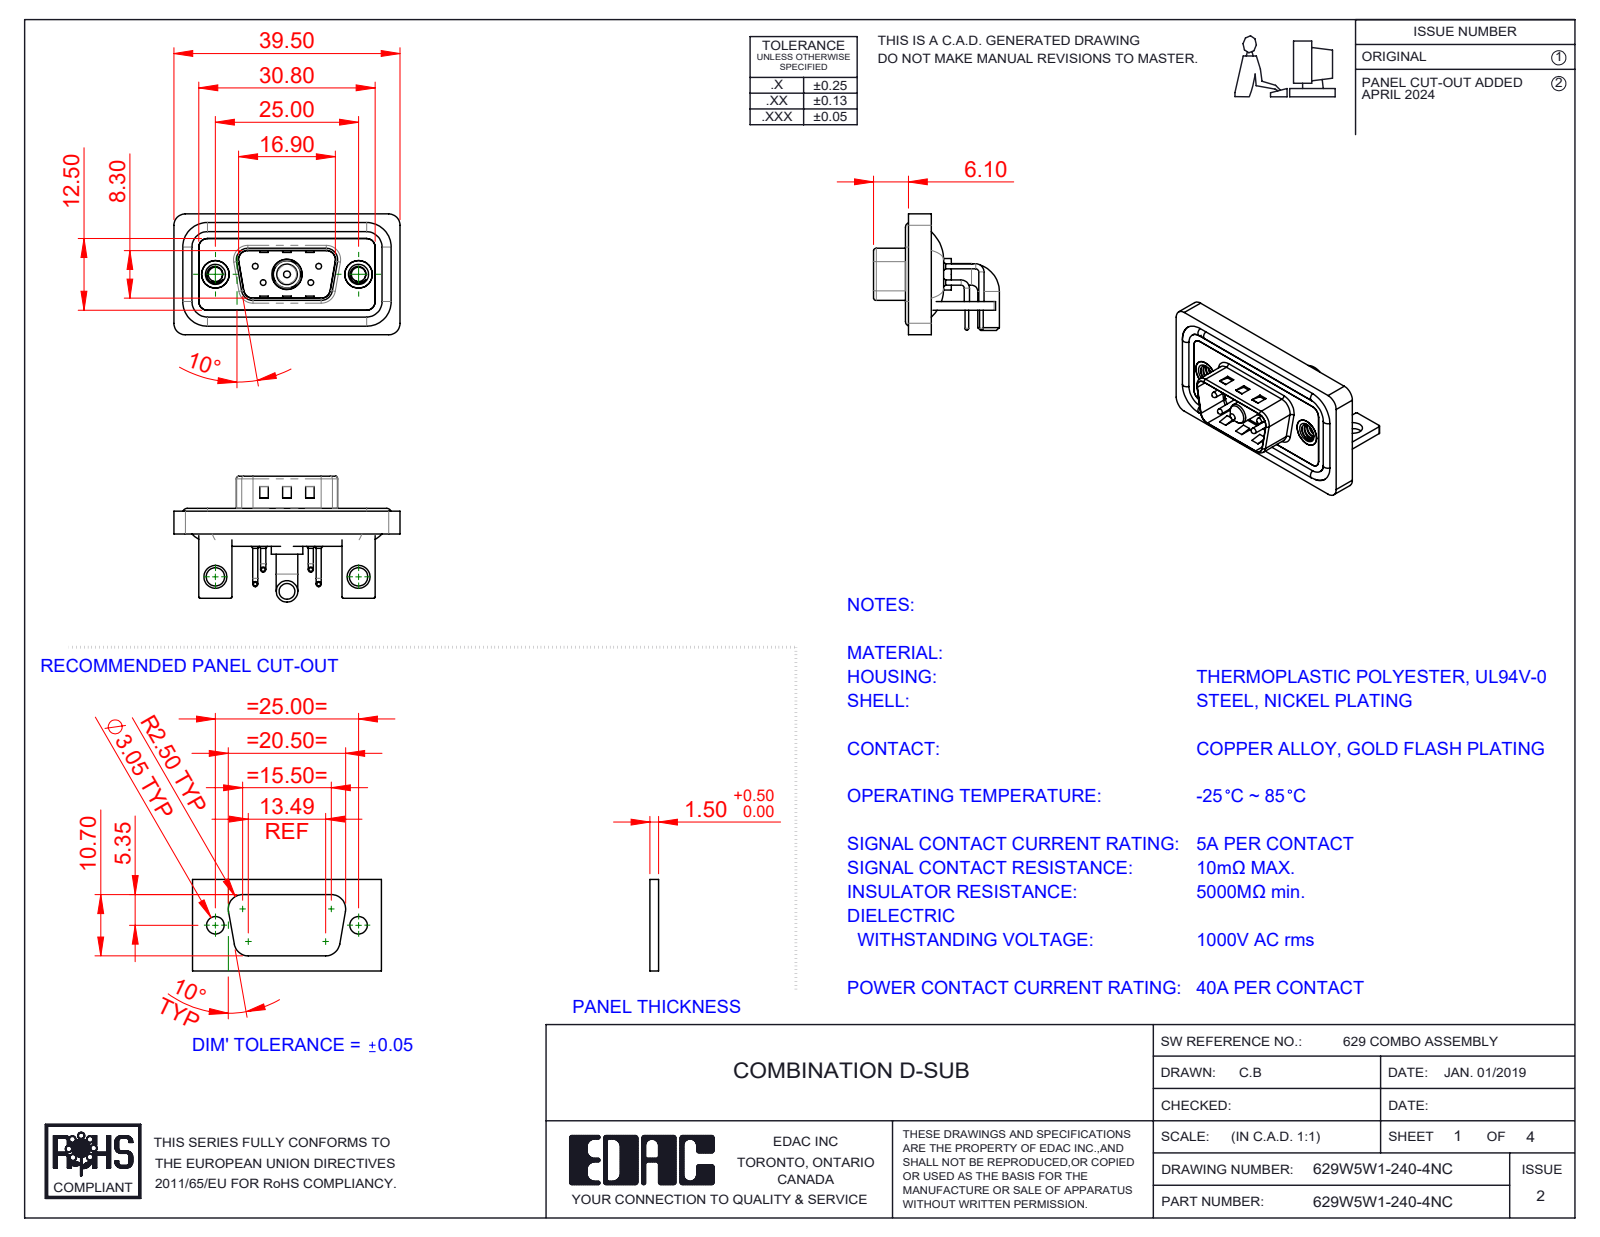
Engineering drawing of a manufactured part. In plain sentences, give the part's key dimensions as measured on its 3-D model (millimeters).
The part is named "629Combo Shell Rear_09 Contacts; 629Combo Housing_5W1; 629Combo Contact Row 1; 629Combo Stabilizer Bracket (+6 more)". Its 3-D file was written by "SolidWorks 2023 (CONFIG_CONTROL_DESIGN)". It is 15 solids with 932 faces: 431 planar, 363 cylindrical and 138 other. Overall it measures 39.5 by 21.98 by 21.1 millimeters. Its volume is 4 821 cubic millimeters and its surface area 7 796 square millimeters. Round holes: 4 of diameter 0.75, 4 of diameter 1.6, 4 of diameter 2, 2 of diameter 2.5, 2 of diameter 3.2, 2 of diameter 4, 2 of diameter 4.8, 2 of diameter 5, 1 of diameter 4.85, 1 of diameter 5.3. Round bosses or shafts: 8 of diameter 0.9, 4 of diameter 1.6, 4 of diameter 1.5, 4 of diameter 1, 4 of diameter 0.65, 2 of diameter 4.9, 2 of diameter 3.75, 1 of diameter 5.5. Partial cylindrical surfaces (rounded edges, fillets, slot ends): 19 of radius 2, 18 of radius 1.5, 16 of radius 0.25, 9 of radius 0.5, 8 of radius 1.6, 4 of radius 0.6, 4 of radius 0.65, 4 of radius 0.9. The main face-to-face distances are 0.4, 1.5, 0.8, 2.9, 1.1, 2.1, 1.2, 1.6, 2.5, 3.7. The hole center spacings are 3.16, 5.72, 7.1, 12.5, 18.1, 25, 4.39, 4.4.
